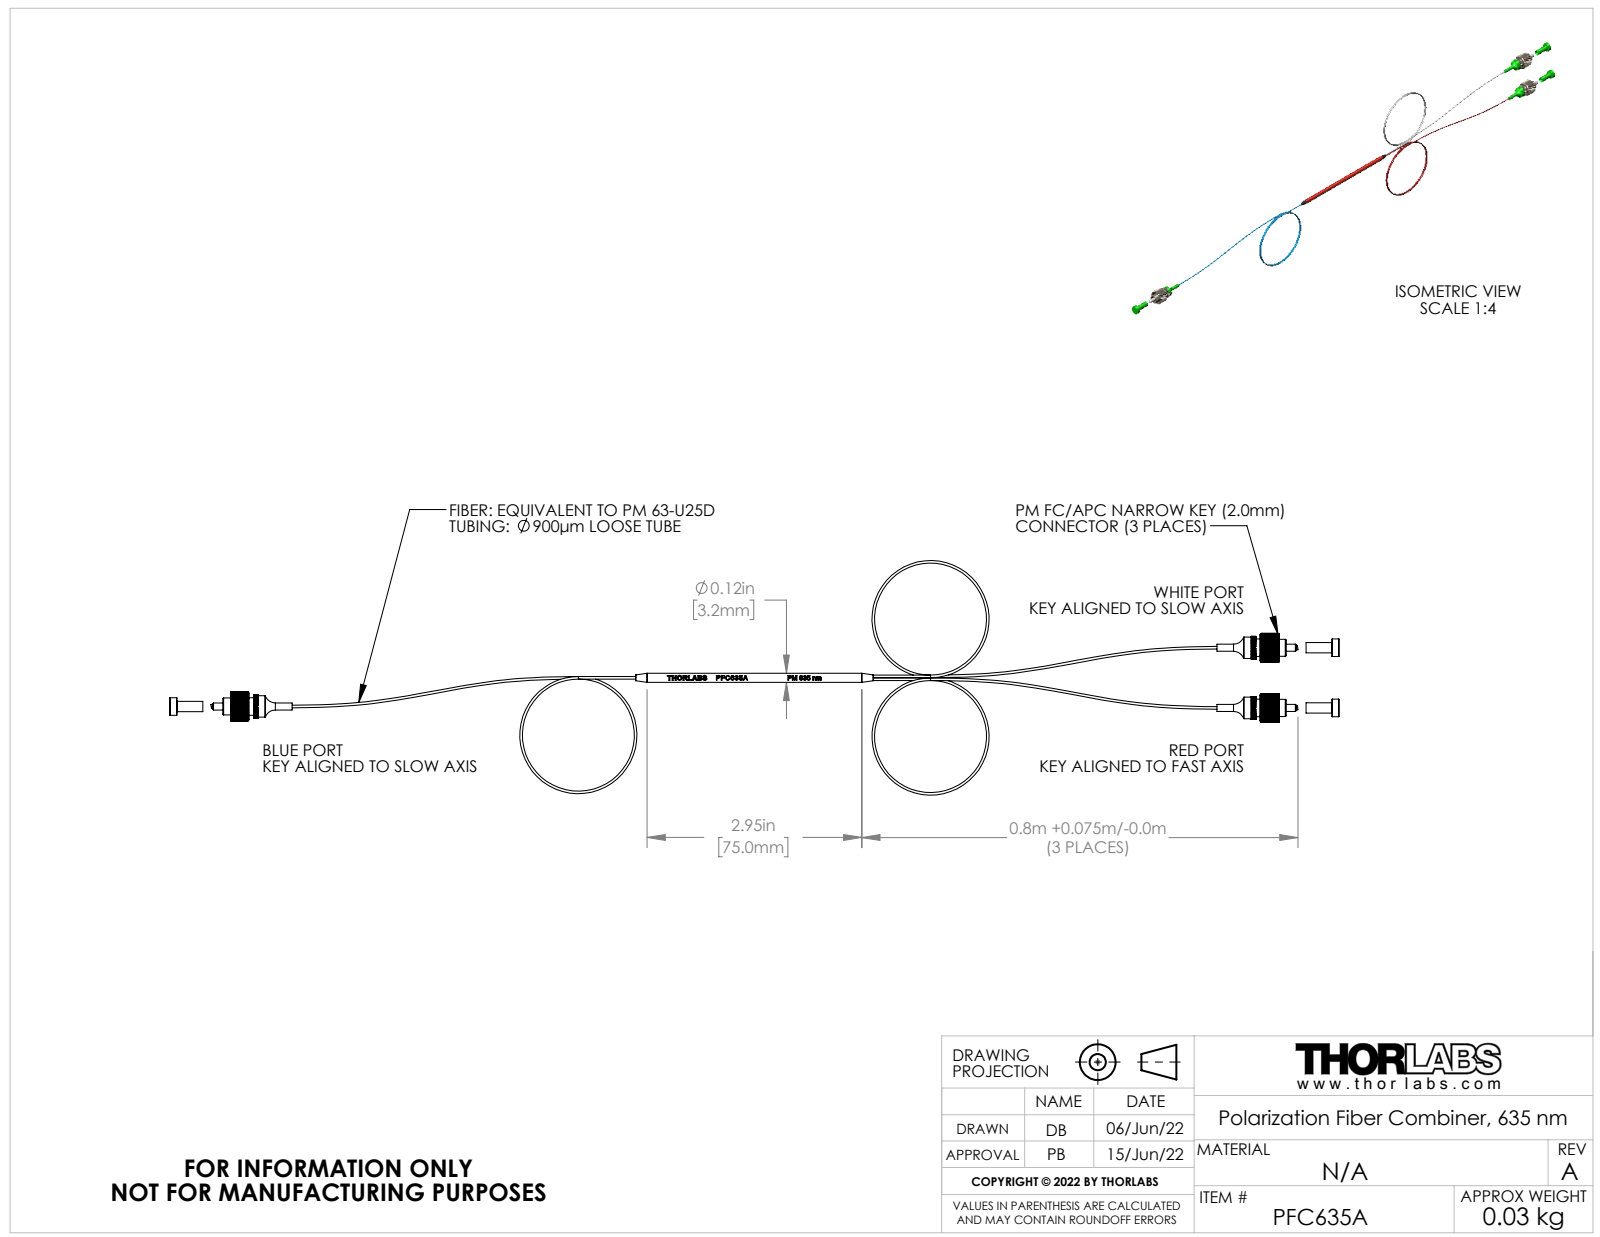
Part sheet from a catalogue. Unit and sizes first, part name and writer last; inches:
Units: inches
Overall size (bounding box): 16.075 × 3.224 × 0.551
Round holes (diameter × count): ⌀0.02 ×6, ⌀0.039 ×5, ⌀0.035 ×3, ⌀0.098 ×3, ⌀0.11 ×3, ⌀0.132 ×3, ⌀0.172 ×3, ⌀0.173 ×3, ⌀0.2 ×3, ⌀0.219 ×3, ⌀0.24 ×3, ⌀0.256 ×3
Round bosses / shafts (diameter × count): ⌀0.295 ×3, ⌀0.278 ×3, ⌀0.243 ×3, ⌀0.239 ×3, ⌀0.234 ×3, ⌀0.212 ×3, ⌀0.191 ×3, ⌀0.142 ×3
Partial cylindrical surfaces — rounded edges, fillets, slot ends (radius × count): R0.02 ×6, R0.03 ×3, R0.061 ×3, R0.089 ×3, R0.157 ×3, R0.197 ×3, R0.018 ×2, R0.039 ×1
Main face-to-face distances: 0.27, 0.27, 0.079, 0.056, 0.196, 13.778, 0.061, 0.117, 0.135, 1.09
Hole centre spacings: 0.402, 0.421, 0.02, 0.44, 0.039, 0.159, 0.382, 0.807
Volume: 0.2 in³ · Surface area: 21.05 in²
Bodies: 32 solids, 2624 faces (1277 planar, 889 cylindrical, 458 other)
Part name (STEP PRODUCT): T09HNT1_Standard; SGP-N4 125.5um APC; SGZ-1A1512F00G_125.5um; DWG1529 (+8 more)
STEP written by: SolidWorks 2020 (CONFIG_CONTROL_DESIGN)
